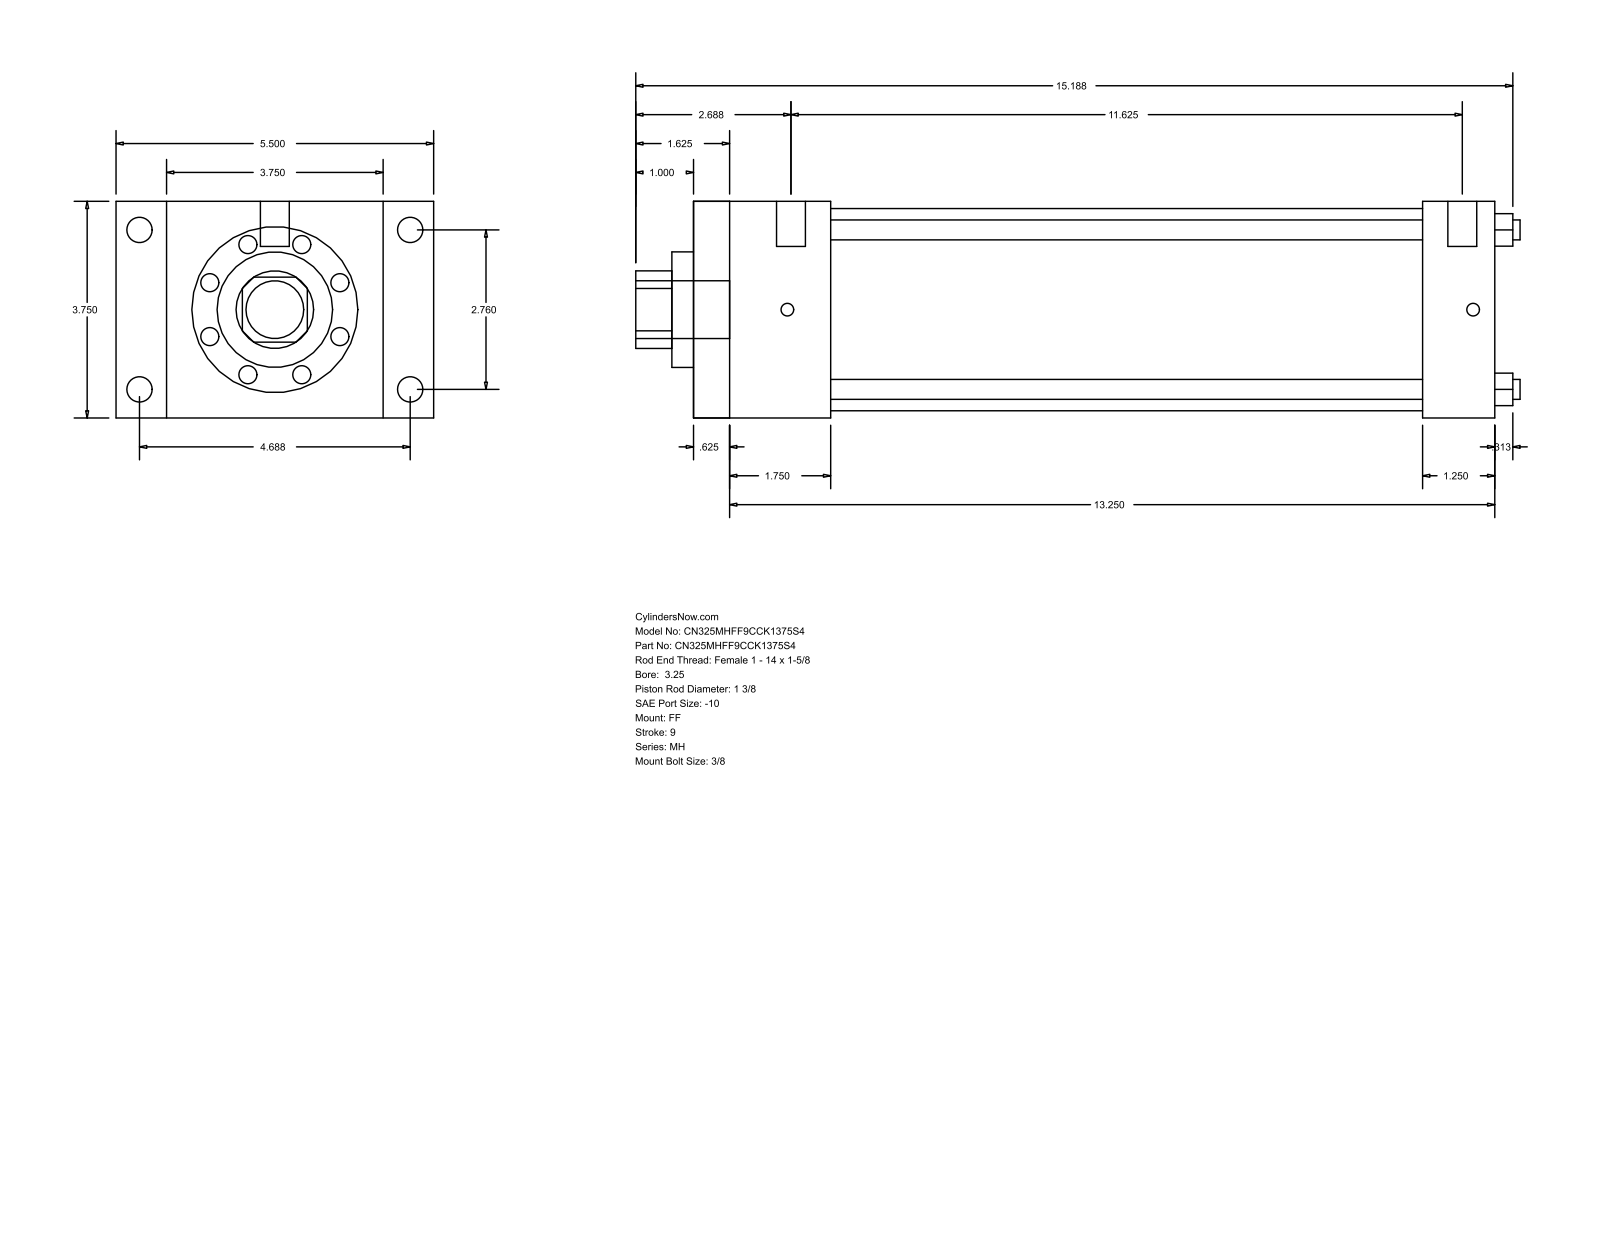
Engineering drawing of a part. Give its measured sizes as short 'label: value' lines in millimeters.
name: MH_FF__0325_1.375
written by: GSSL Pune (CONFIG_CONTROL_DESIGN)
unit: mm
bodies: 0 solids, 92 faces (64 planar, 28 cylindrical, 0 other)
size: 388.94 × 139.7 × 95.25
holes: 4× ⌀8.76, 1× ⌀34.92, 1× ⌀50.8, 1× ⌀88.9
bosses: 4× ⌀11.13, 4× ⌀5.56, 2× ⌀12.7, 1× ⌀25.4
rounds: 1× R17.06
face distances: 95.24, 352.42, 15.87, 336.55, 22.23, 117.47, 320.67, 304.8, 31.75, 60.32
hole spacings: 49.57, 70.1, 99.14
